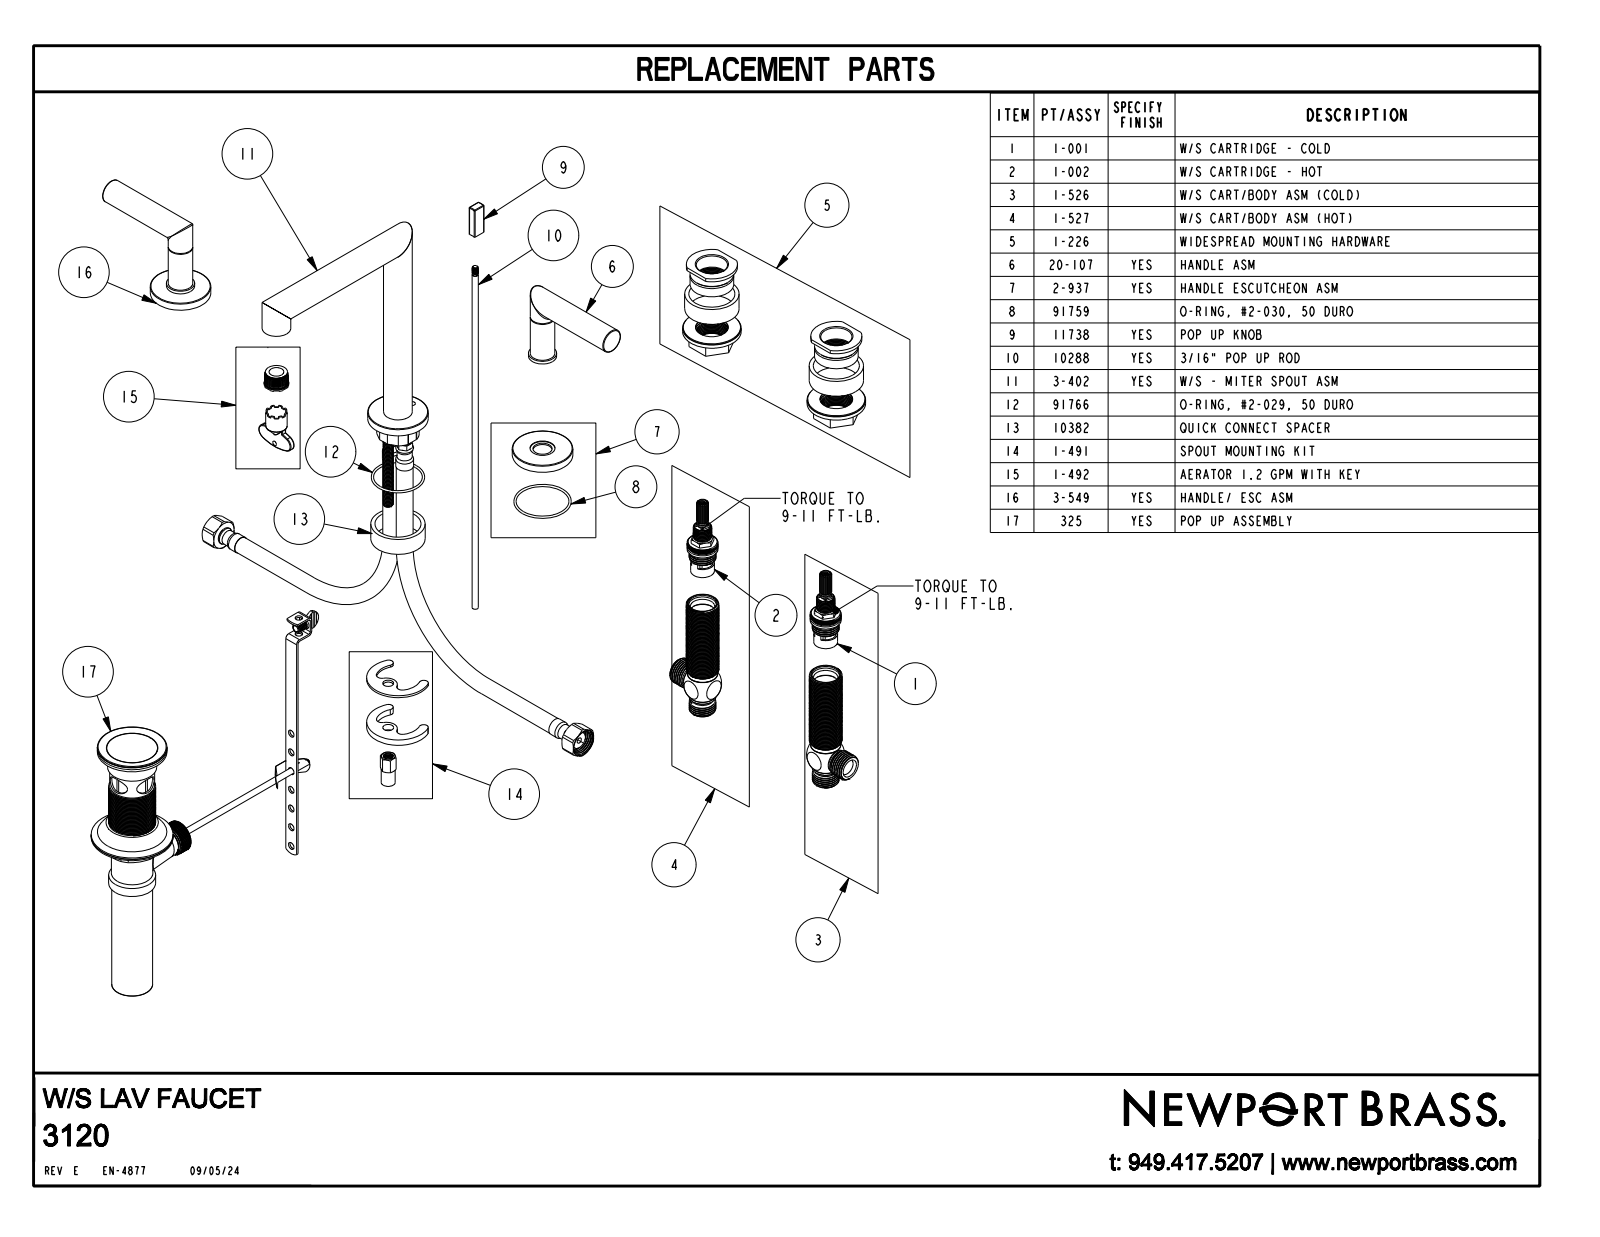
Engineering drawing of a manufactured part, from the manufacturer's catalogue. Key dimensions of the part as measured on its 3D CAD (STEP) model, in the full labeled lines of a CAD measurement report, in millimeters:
Part name (STEP PRODUCT): 3120
STEP written by: CREO PARAMETRIC BY PTC INC, 2018400 (CONFIG_CONTROL_DESIGN)
Units: millimetres
Bodies: 3 solids, 95 faces (23 planar, 44 cylindrical, 28 other)
Overall size (bounding box): 355.6 × 180.1 × 168
Volume: 229 400 mm³ · Surface area: 52 520 mm²
Round bosses / shafts (diameter × count): ⌀47 ×3, ⌀22.2 ×3, ⌀19.1 ×3, ⌀21.8 ×2, ⌀12.9 ×2
Partial cylindrical surfaces — rounded edges, fillets, slot ends (radius × count): R0.5 ×6, R11.9 ×1, R22.3 ×1
Main face-to-face distances: 6.4, 174.6, 181, 152.4, 146.1, 43.2, 44, 36.9, 37.6, 0.8
